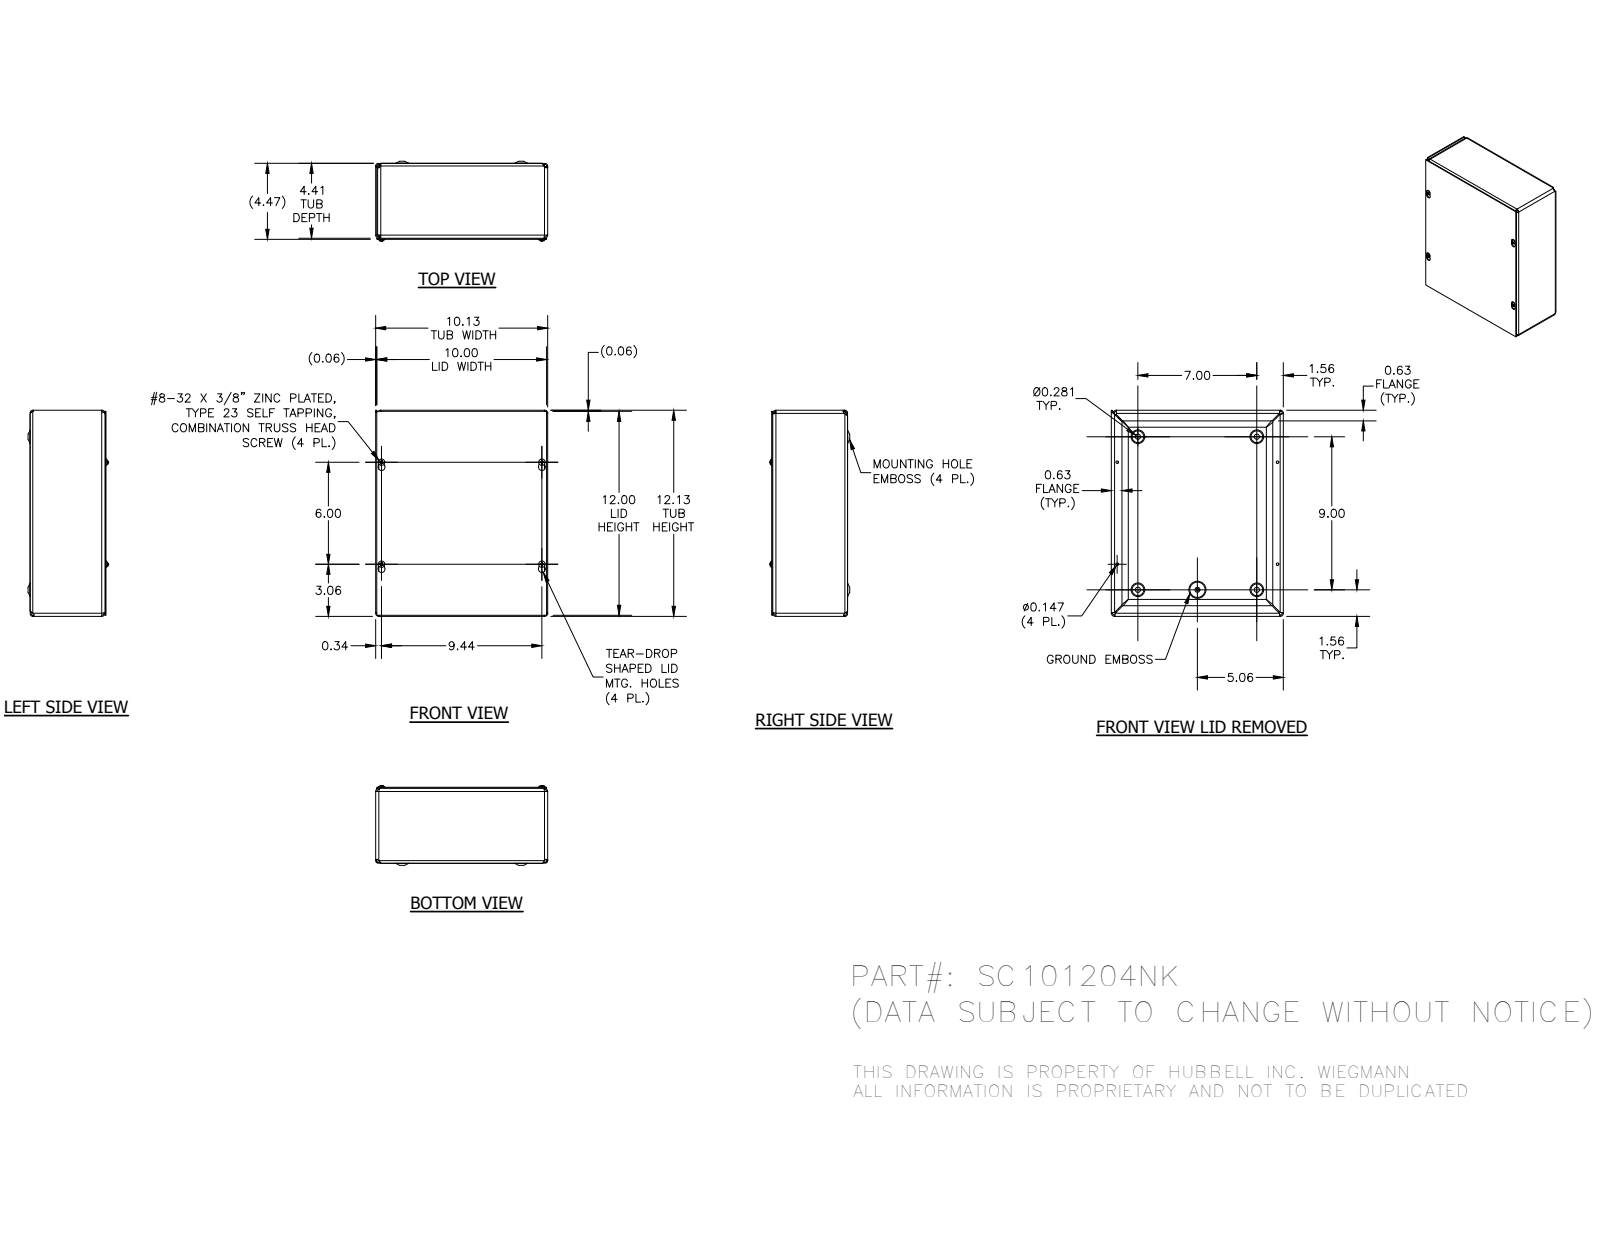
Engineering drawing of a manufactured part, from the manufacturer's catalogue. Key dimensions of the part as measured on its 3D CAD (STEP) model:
Part name (STEP PRODUCT): SC1012BKP; SC101204NKWRA; SC1012LID; 34056 (+1 more)
STEP written by: Autodesk Inventor 2014 (AUTOMOTIVE_DESIGN)
Units: millimetres
Bodies: 7 solids, 357 faces (132 planar, 67 cylindrical, 158 other)
Overall size (bounding box): 307.98 × 257.18 × 119.2
Volume: 492 501 mm³ · Surface area: 632 986 mm²
Round holes (diameter × count): ⌀3.73 ×4, ⌀7.62 ×4, ⌀4.19 ×1
Round bosses / shafts (diameter × count): ⌀9.75 ×4, ⌀4.17 ×4, ⌀5.8 ×1
Partial cylindrical surfaces — rounded edges, fillets, slot ends (radius × count): R3.17 ×12, R4.75 ×8, R1.4 ×4, R1.57 ×4, R2.38 ×4, R2.97 ×4, R3.15 ×4, R3.96 ×4
Main face-to-face distances: 1.57, 110.32, 111.89, 1.59, 111.91, 113.48, 1.58, 257.18, 255.61, 255.6
Hole centre spacings: 49.09, 193, 282.61, 88.9, 152.4, 177.8, 212.2, 212.21
